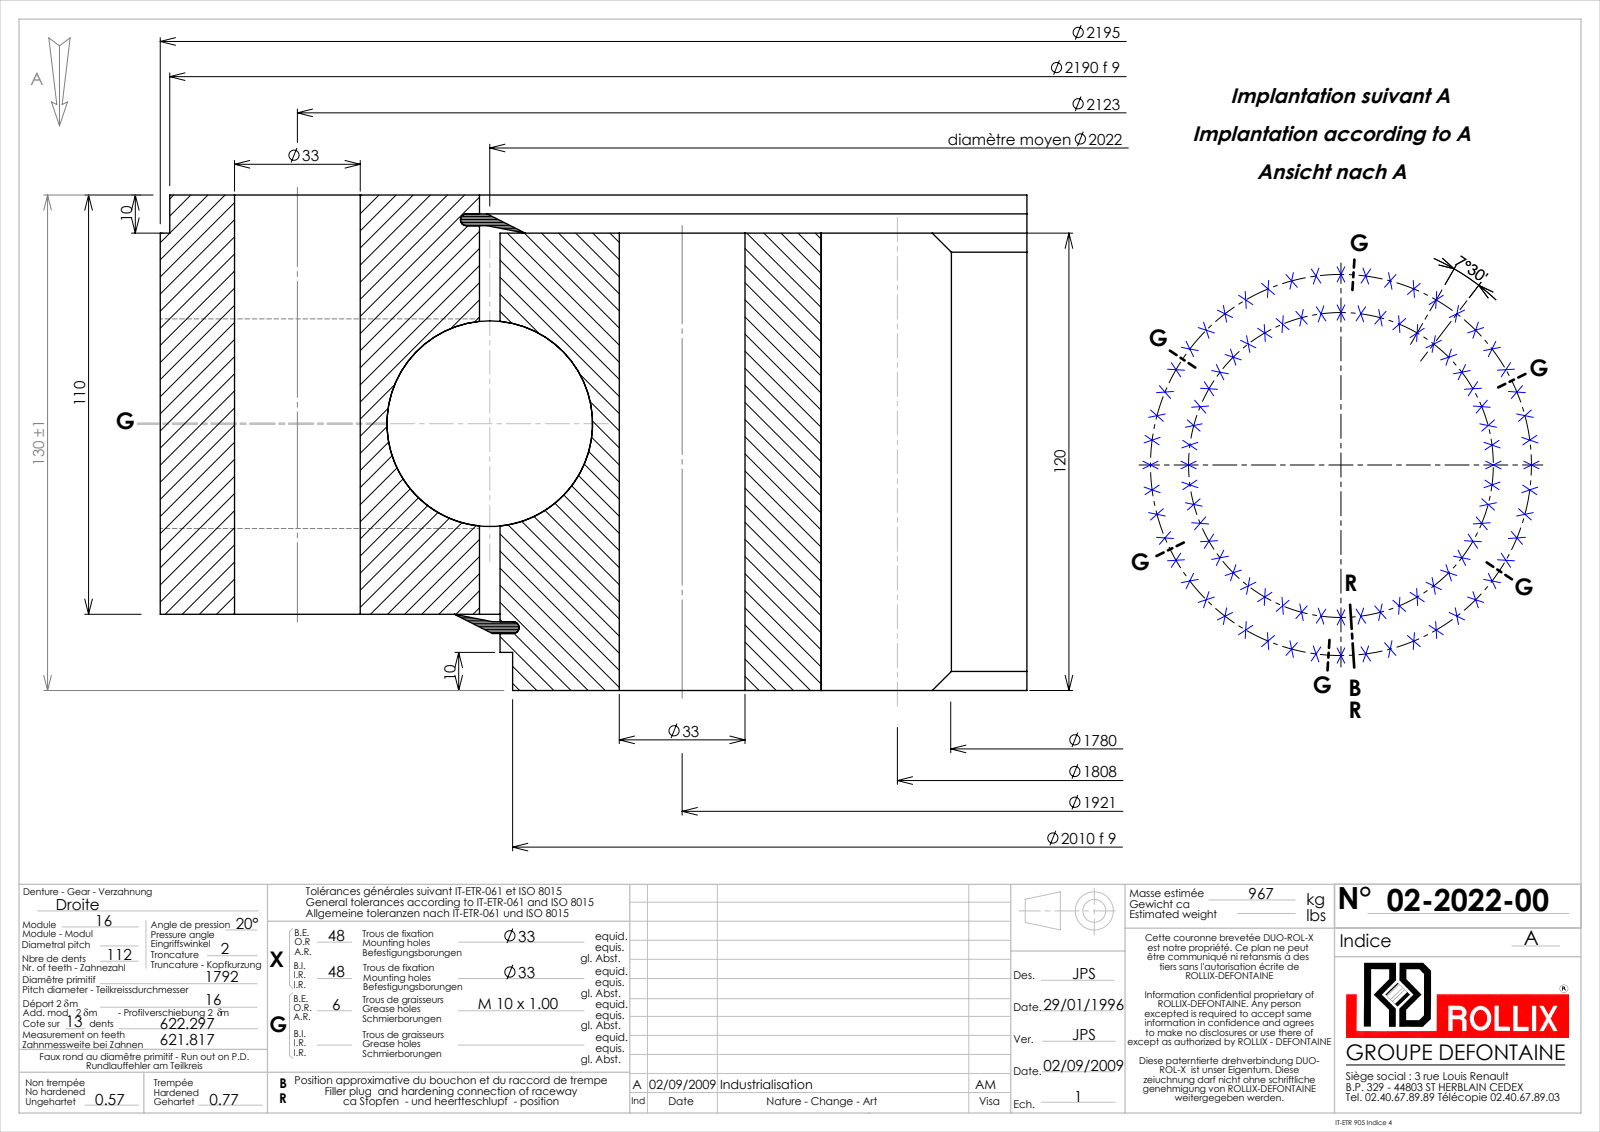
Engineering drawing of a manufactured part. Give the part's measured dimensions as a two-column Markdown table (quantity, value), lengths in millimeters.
| quantity | value |
| --- | --- |
| part name | 02-2022-00 |
| STEP written by | SolidWorks 2016 (CONFIG_CONTROL_DESIGN) |
| units | millimeters |
| bodies | 5 solids, 937 faces (238 planar, 447 cylindrical, 252 other) |
| overall size | 2195 × 2195 × 130 |
| volume | 113 000 000 mm³ |
| surface area | 7 772 000 mm² |
| round holes (diameter × count) | 33 × 96, 9 × 6, 2027.4 × 1 |
| round bosses / shafts (diameter × count) | 2195 × 1, 2190 × 1, 2016.6 × 1, 2010 × 1 |
| partial cylindrical surfaces (radius × count) | 890 × 1, 924 × 1 |
| main face-to-face distances | 120, 10, 110, 20, 100, 130, 5.05, 105.05, 1.95, 101.95 |
| hole center spacings | 125.64, 374.77, 250.74, 497.19, 735.14, 849.64, 617.49, 1266.61 |
